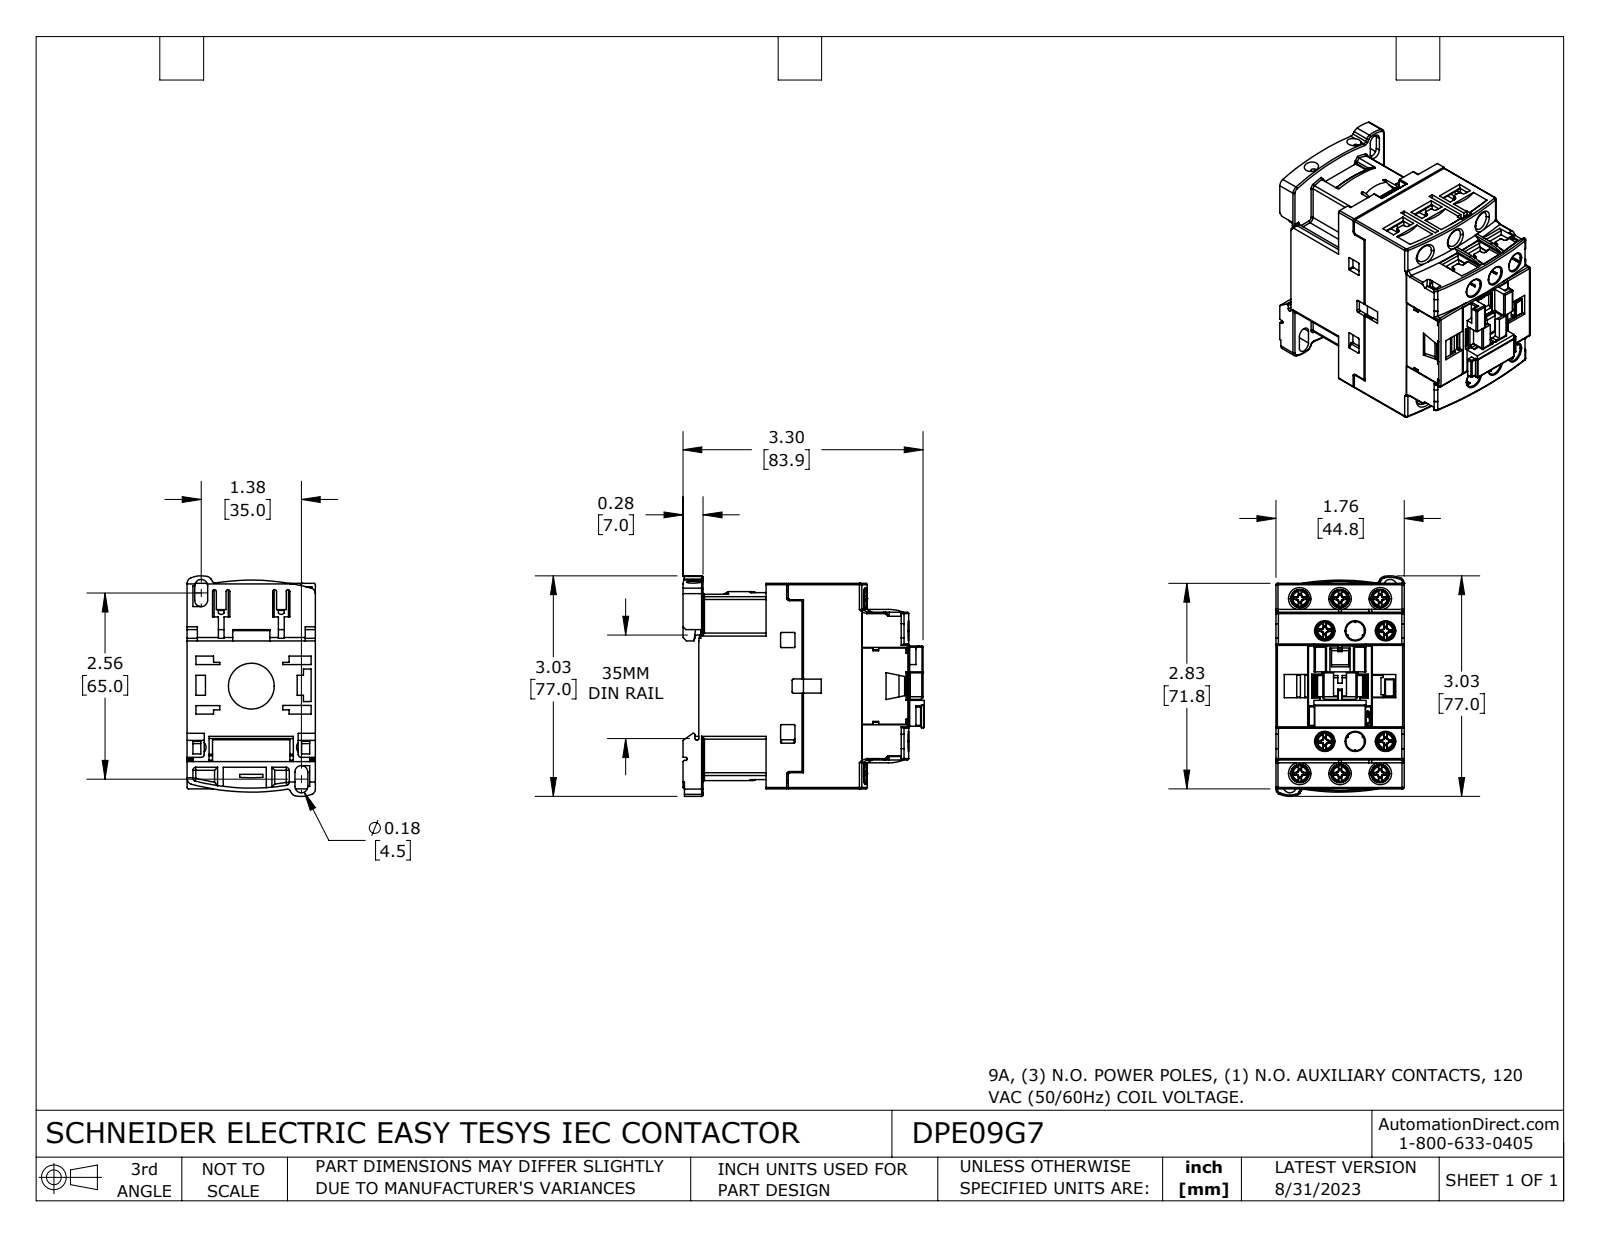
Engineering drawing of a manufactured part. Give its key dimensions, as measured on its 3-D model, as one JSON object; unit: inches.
{"part_name": "DPE09G7", "step_written_by": "SolidWorks 2021 (CONFIG_CONTROL_DESIGN)", "units": "inches", "bodies": {"solids": 20, "faces": 3363, "planar": 2297, "cylindrical": 694, "other": 372}, "overall_size": [3.317, 3.031, 1.783], "volume_in3": 8.907, "surface_area_in2": 103.4, "round_holes": [[0.252, 6], [0.256, 6], [0.197, 2], [0.167, 1], [0.63, 1]], "round_bosses_or_shafts": [[0.138, 10], [0.108, 10], [0.315, 6]], "partial_cylinders_radius": [[0.02, 78], [0.012, 64], [0.039, 61], [0.006, 42], [0.016, 24], [0.63, 9], [0.024, 8], [0.079, 7]], "face_to_face_distances": [0.047, 1.764, 1.717, 0.321, 1.128, 0.807, 0.35, 2.78, 1.366, 1.118], "hole_center_spacings": [0.417, 0.488, 0.551, 0.558, 0.788, 0.878, 1.321, 1.576]}
